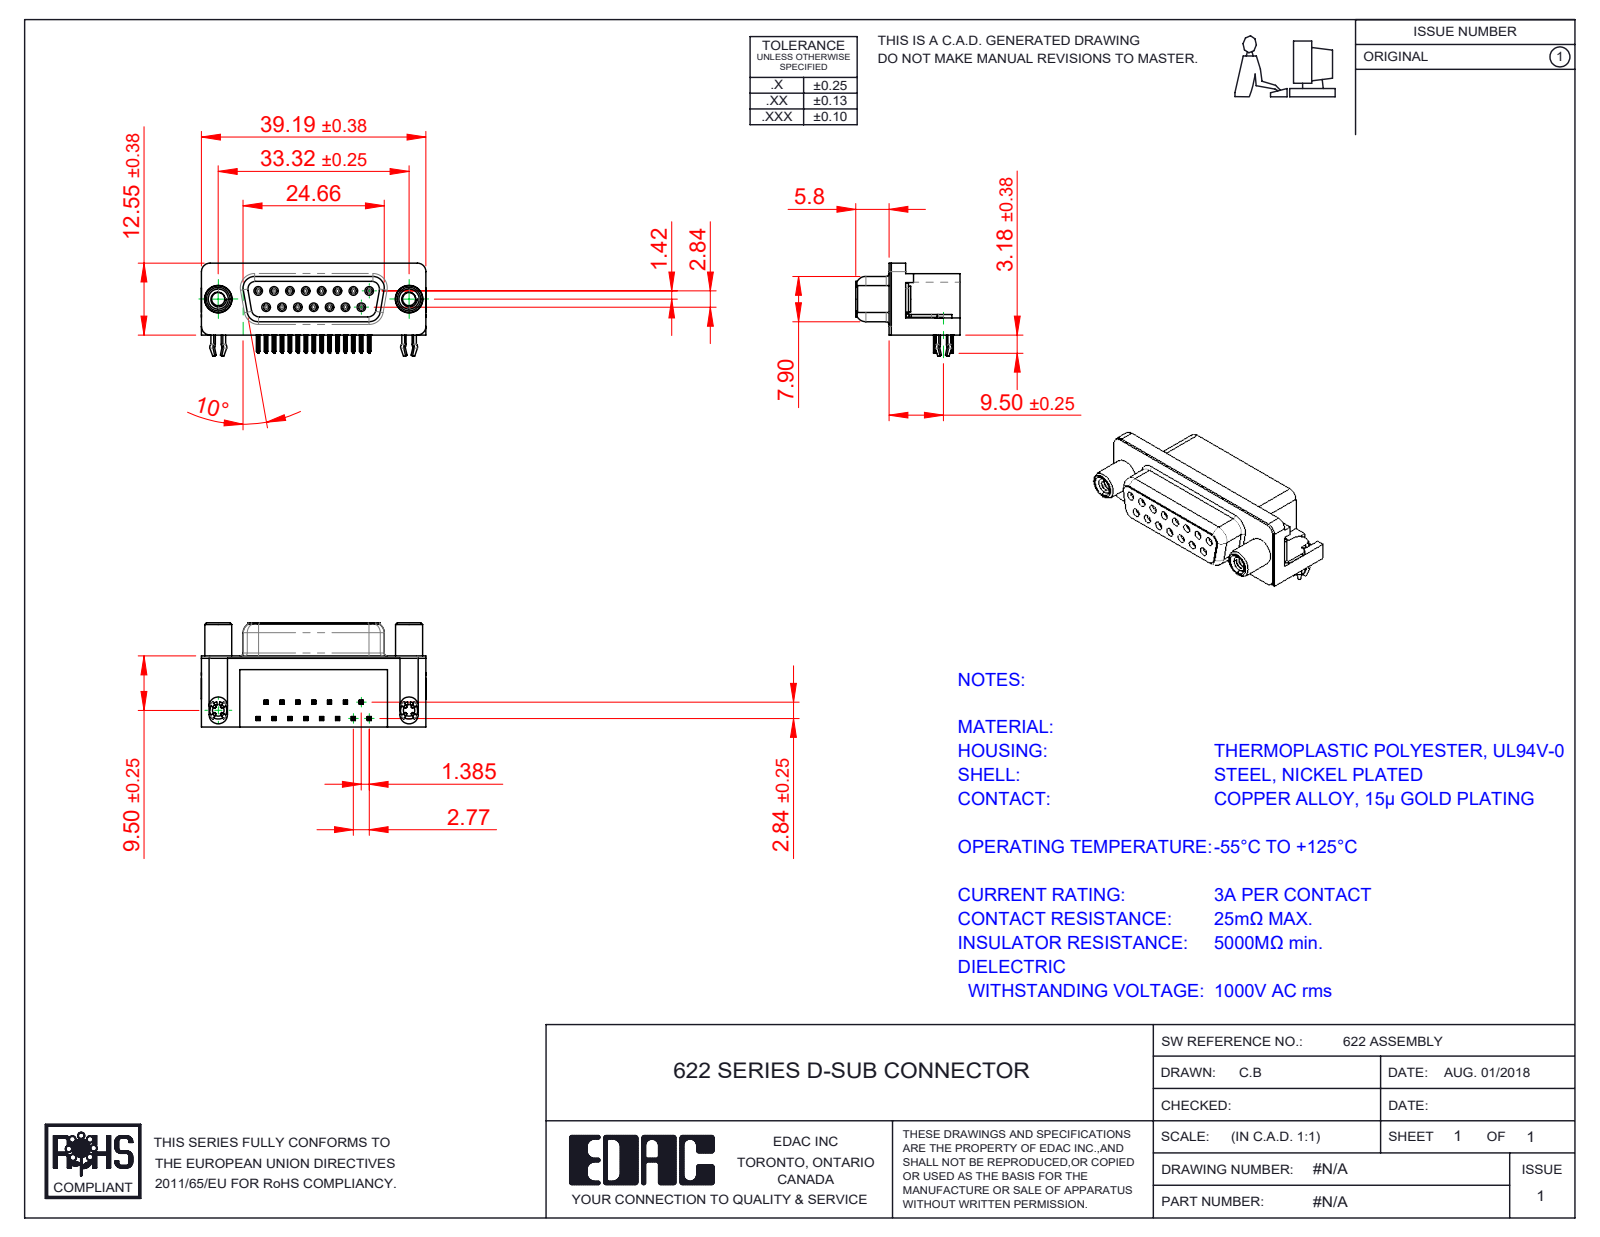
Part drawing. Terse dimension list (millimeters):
name: 622-015-368-550; 622 Socket Bottom; 622 Contact Top; 622 Round Threaded Standoff (+3 more)
written by: SolidWorks 2016 (CONFIG_CONTROL_DESIGN)
unit: mm
bodies: 21 solids, 2451 faces (1066 planar, 625 cylindrical, 760 other)
size: 39.22 × 18.2 × 15.73
volume: 5 290 mm³; area: 6 994 mm²
holes: 15× ⌀0.8, 15× ⌀0.9, 2× ⌀2.26, 2× ⌀2.3, 2× ⌀3.1, 2× ⌀4, 2× ⌀4.8, 2× ⌀5
bosses: 15× ⌀1.2, 2× ⌀4.9, 2× ⌀4.7, 2× ⌀4.5, 2× ⌀3.85, 2× ⌀3.26
rounds: 120× R0.1, 60× R0.15, 30× R0.35, 18× R1, 15× R0.34, 8× R1.35, 8× R1.5, 8× R1.6
face distances: 0.4, 12, 6.2, 10.35, 12.4, 2.9, 6.65, 0.85, 0.35, 5.8
hole spacings: 3.16, 2.77, 5.54, 8.31, 11.08, 5.03, 5.04, 7.48
